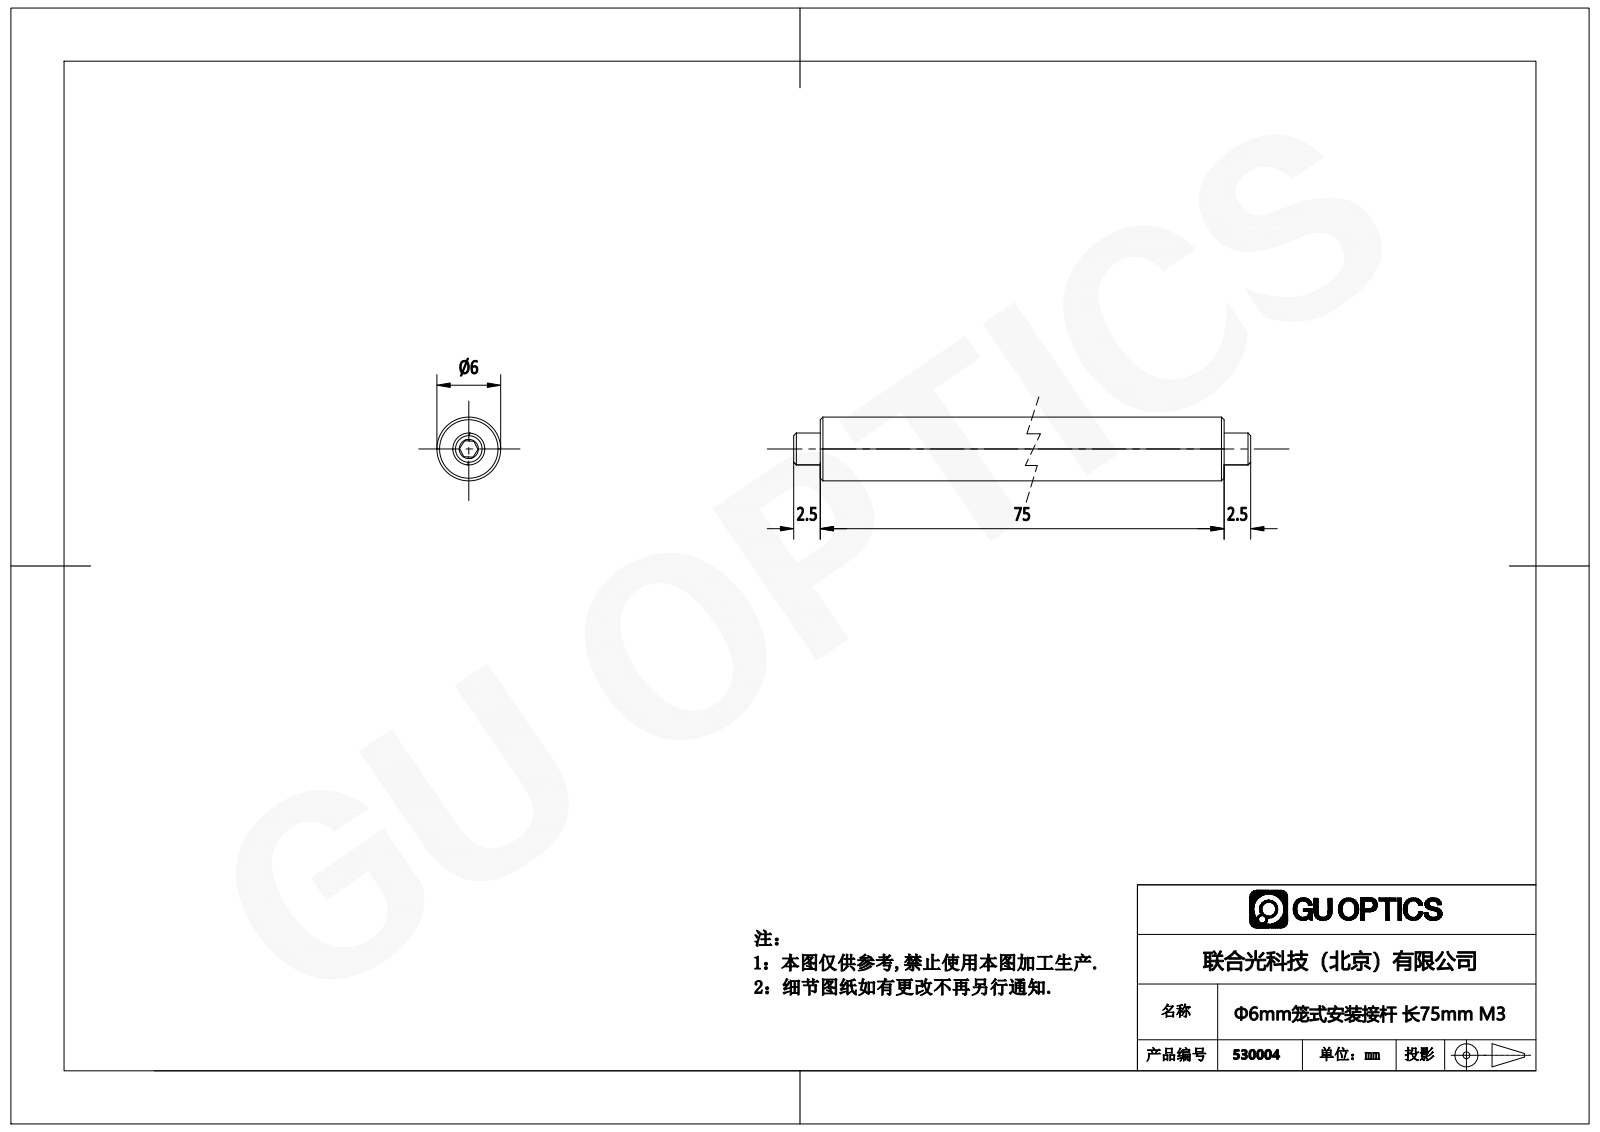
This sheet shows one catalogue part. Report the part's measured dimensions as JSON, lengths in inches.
{"step_written_by": "SolidWorks 2018 (AUTOMOTIVE_DESIGN)", "units": "inches", "bodies": {"solids": 0, "faces": 36, "planar": 18, "cylindrical": 6, "other": 12}, "overall_size": [3.15, 0.236, 0.236], "round_bosses_or_shafts": [[0.236, 1], [0.118, 1]], "face_to_face_distances": [2.953, 0.059, 0.098, 3.051, 0.039, 3.11, 3.012, 3.15, 3.071]}
